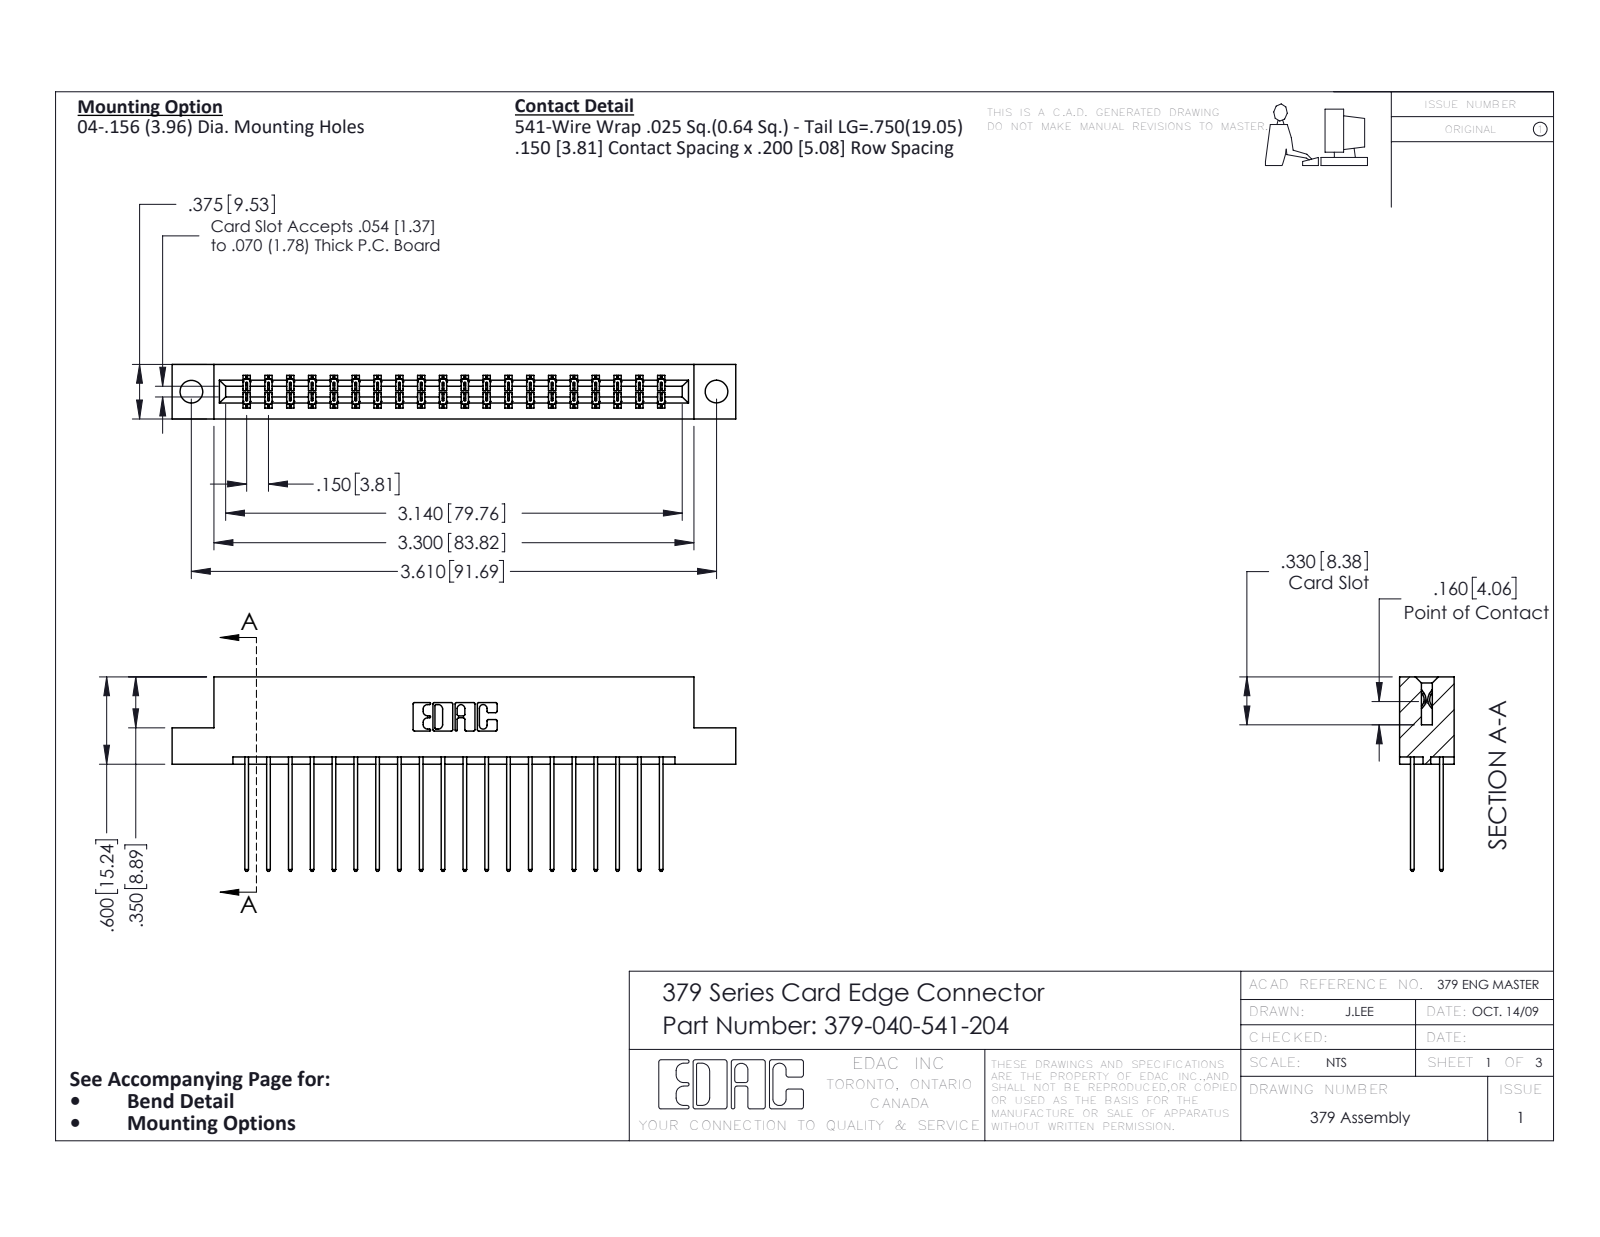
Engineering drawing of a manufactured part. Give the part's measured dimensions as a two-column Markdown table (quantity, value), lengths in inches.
| quantity | value |
| --- | --- |
| part name | 379-040-541-204; 345-292-001_345-293-141; 379 Part_Flush - .156 Dia - TH |
| STEP written by | SolidWorks 2016 (CONFIG_CONTROL_DESIGN) |
| units | inches |
| bodies | 41 solids, 2194 faces (1510 planar, 684 cylindrical, 0 other) |
| overall size | 3.875 × 1.337 × 0.375 |
| volume | 0.632 in³ |
| surface area | 19.18 in² |
| round holes (diameter × count) | 0.156 × 2 |
| partial cylindrical surfaces (radius × count) | 0.006 × 60, 0.01 × 40, 0.01 × 22, 0.007 × 6, 0.031 × 6, 0.026 × 3, 0.014 × 2, 0.022 × 2 |
| main face-to-face distances | 0.3, 0.075, 0.2, 0.1, 0.375, 0.275, 0.025, 0.076, 0.15, 0.225 |
| hole center spacings | 3.61 |
